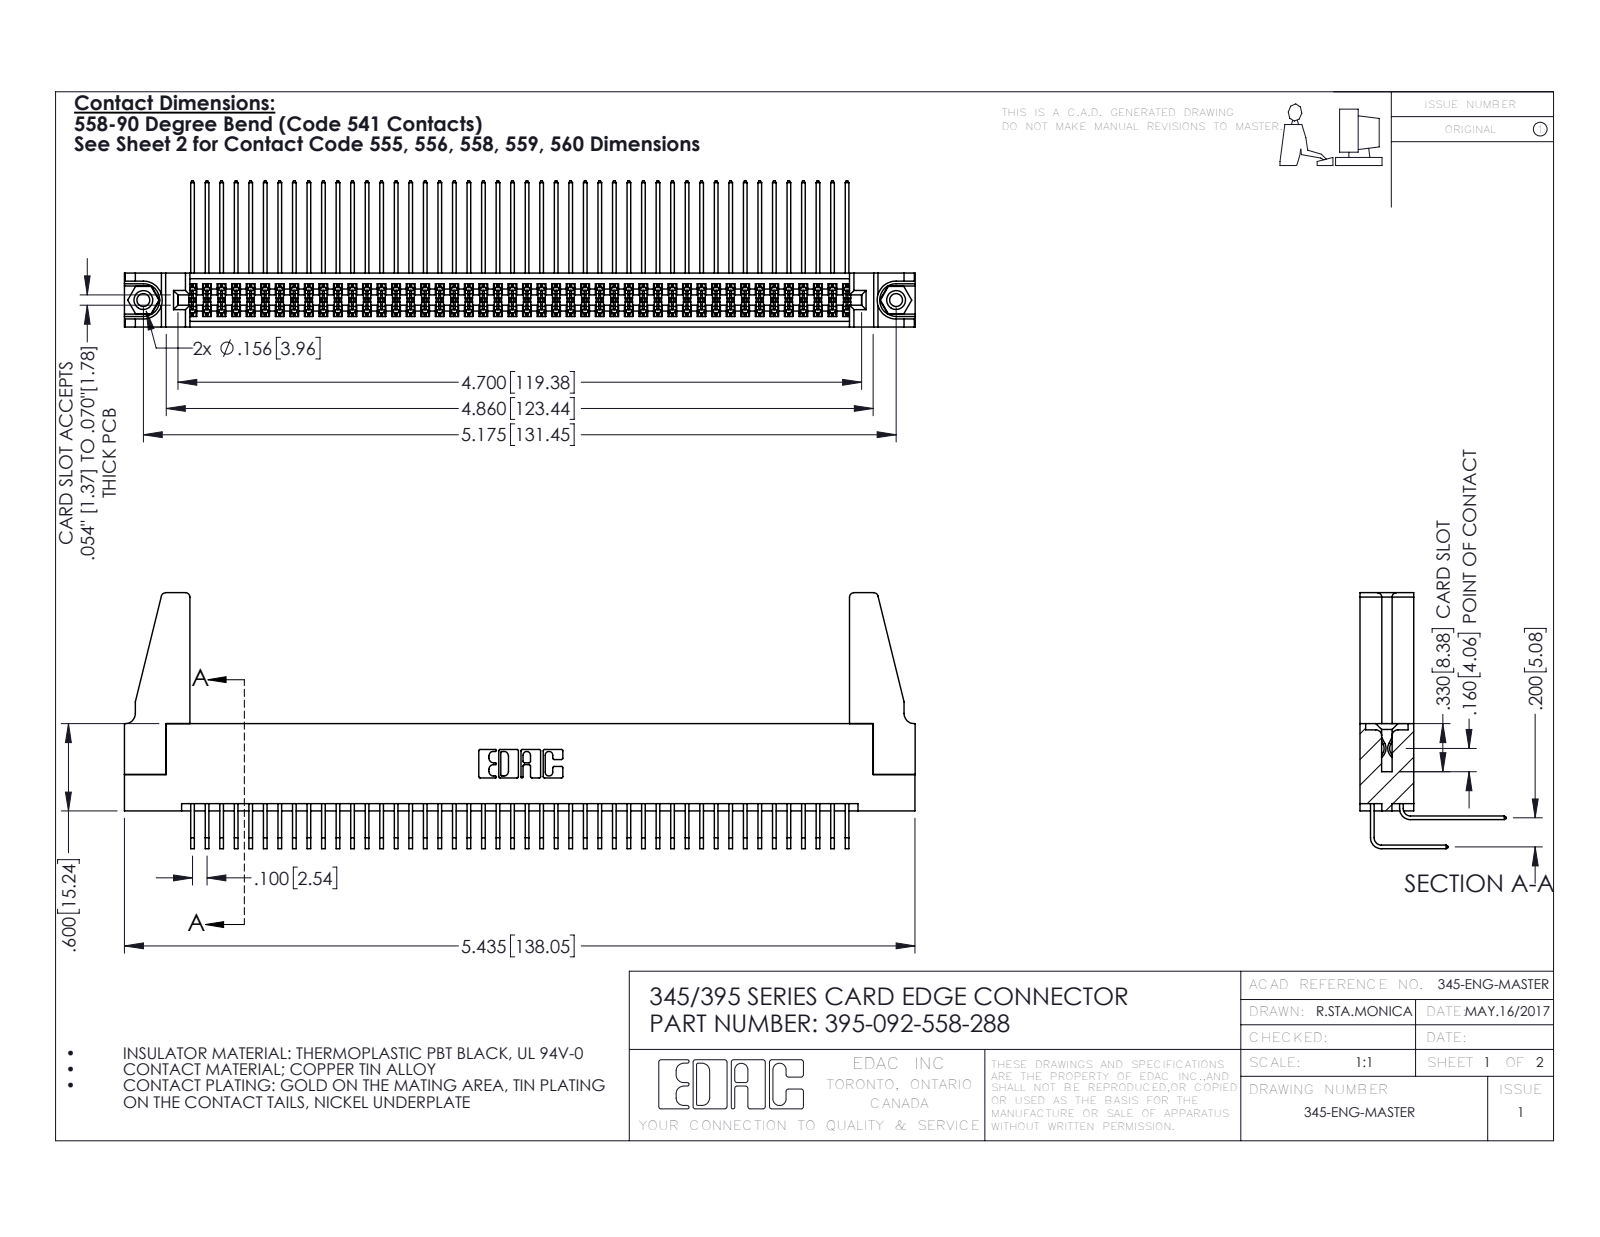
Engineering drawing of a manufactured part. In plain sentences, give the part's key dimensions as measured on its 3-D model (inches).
The part is named "345-220-078_345-220-088; 345-292-001_558 559 Tail - 1; 395-092-558-288; 345 Part_Flush Mounting Lugs - 0.156 Dia-TH (+2 more)". Its 3-D file was written by "SolidWorks 2016 (CONFIG_CONTROL_DESIGN)". It is 97 solids with 5034 faces: 3372 planar, 1646 cylindrical and 16 other. Overall it measures 5.436 by 1.759 by 1.005 inches. Its volume is 1.052 cubic inches and its surface area 40.86 square inches. Round holes: 2 of diameter 0.089, 2 of diameter 0.125, 2 of diameter 0.156, 1 of diameter 0.064. Round bosses or shafts: 2 of diameter 0.155. Partial cylindrical surfaces (rounded edges, fillets, slot ends): 139 of radius 0.006, 22 of radius 0.01, 8 of radius 0.03, 6 of radius 0.007, 6 of radius 0.031, 3 of radius 0.026, 2 of radius 0.014, 2 of radius 0.019. The main face-to-face distances are 0.072, 0.298, 0.2, 0.37, 0.098, 0.272, 0.025, 0.225, 0.285, 0.025. The hole center spacings are 0.27, 4.939, 5.175.
